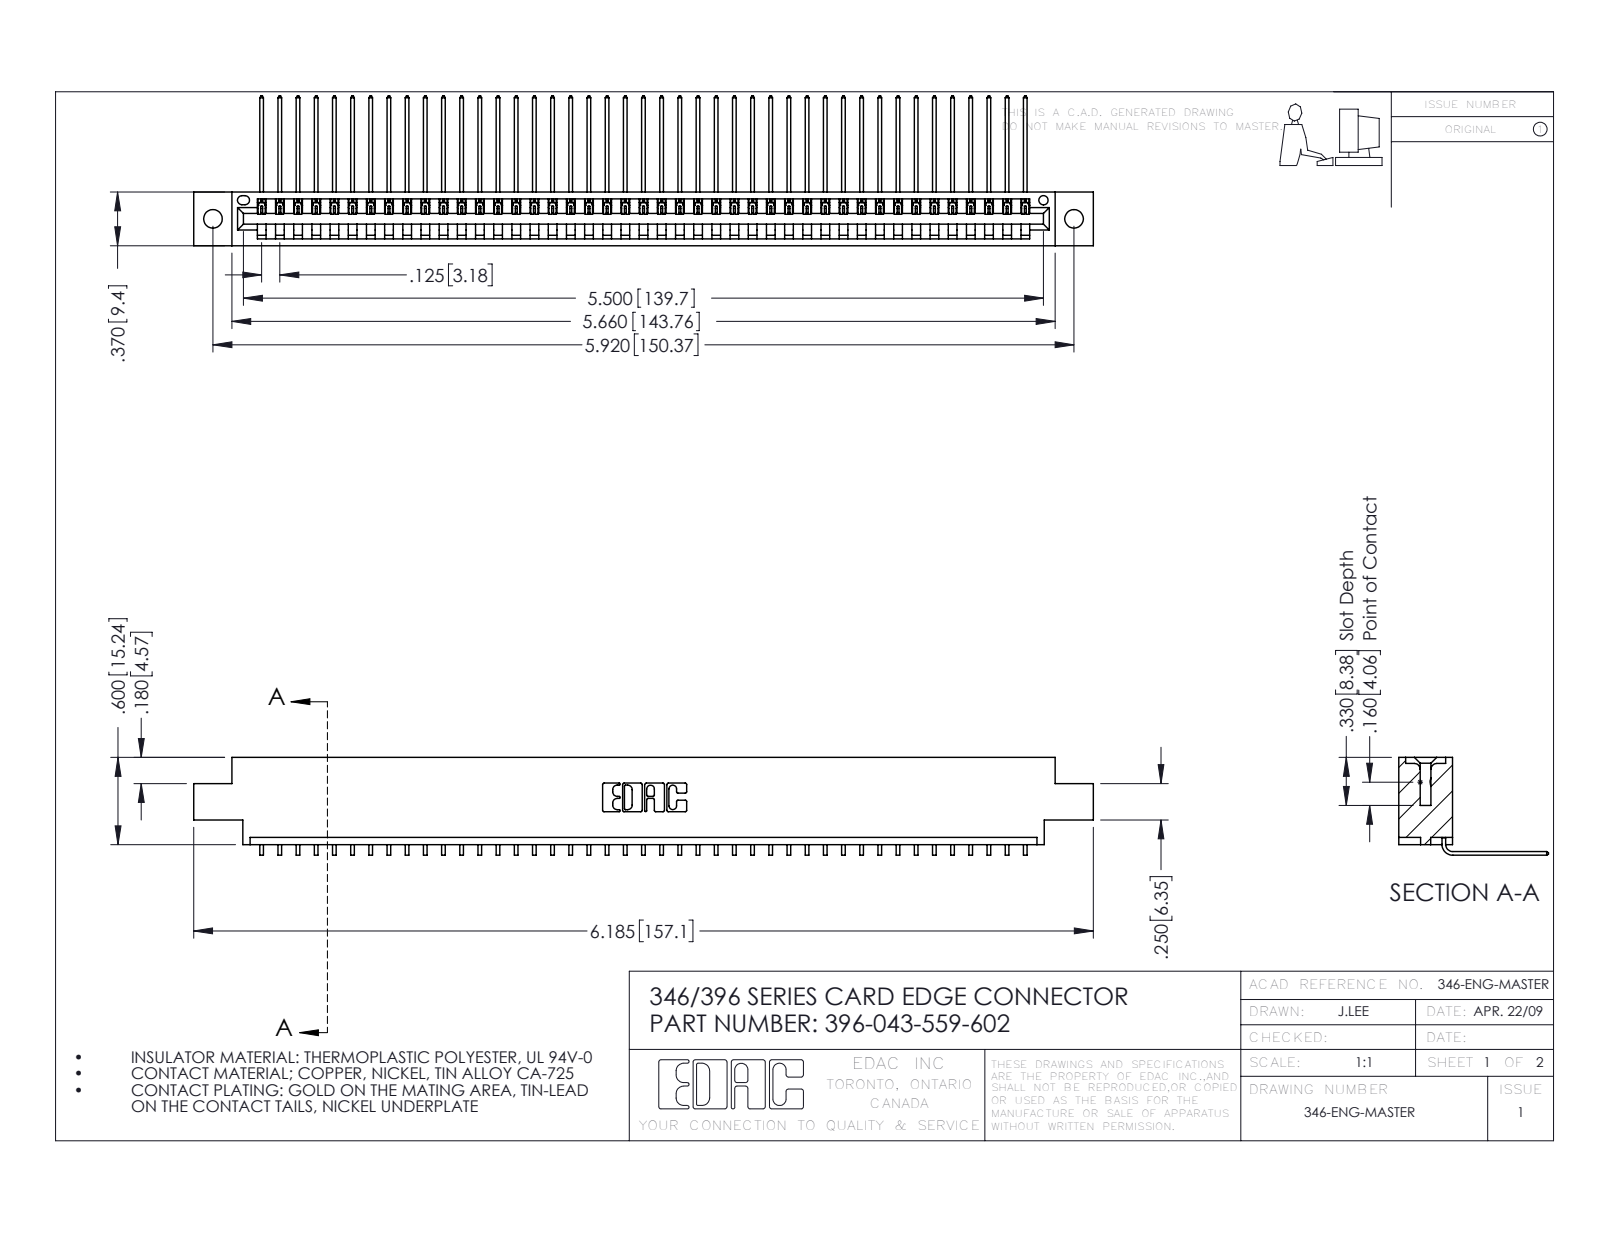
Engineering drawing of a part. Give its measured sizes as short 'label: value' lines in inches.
name: 396-043-559-602; 346 Part_0.170 Offset - 0.128 Dia; 345-292-001_558 559 Tail - 1
written by: SolidWorks 2016 (CONFIG_CONTROL_DESIGN)
unit: in
bodies: 44 solids, 2706 faces (1886 planar, 820 cylindrical, 0 other)
size: 6.185 × 1.03 × 0.673
volume: 0.915 in³; area: 30.22 in²
holes: 2× ⌀0.128, 1× ⌀0.064
rounds: 86× R0.006, 22× R0.01, 6× R0.007, 6× R0.031, 3× R0.026, 2× R0.031, 2× R0.04, 1× R0.014
face distances: 0.048, 0.322, 0.37, 0.025, 0.25, 0.072, 0.298, 0.148, 0.222, 0.1
hole spacings: 0.246, 5.711, 5.92
